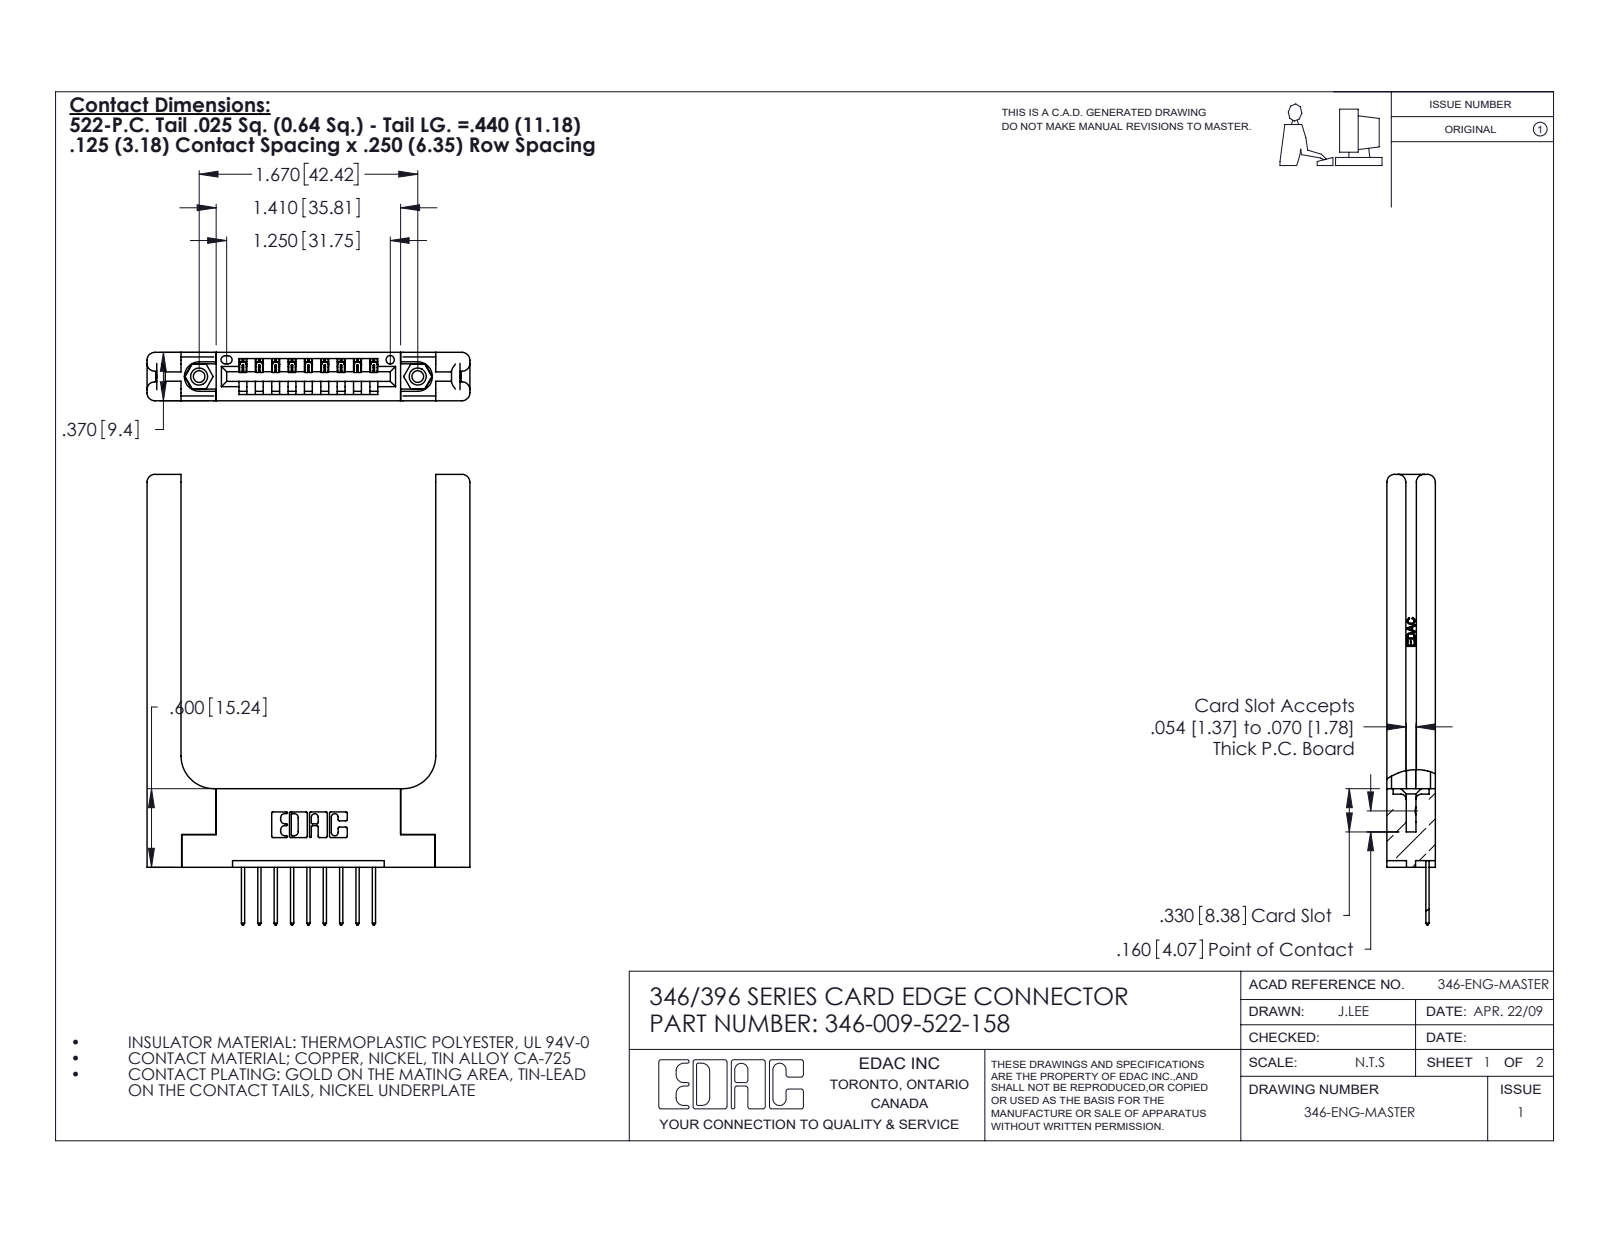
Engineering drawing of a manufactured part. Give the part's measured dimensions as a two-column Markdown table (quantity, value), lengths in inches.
| quantity | value |
| --- | --- |
| part name | 345-250-001_345-250-001-102; 346 Part_Flush Mounting Lugs - 0.156 Dia-TH; 346-220-058_345-220-058; 346-009-522-158 (+1 more) |
| STEP written by | SolidWorks 2020 (CONFIG_CONTROL_DESIGN) |
| units | inches |
| bodies | 14 solids, 914 faces (598 planar, 256 cylindrical, 60 other) |
| overall size | 3.44 × 2.466 × 0.37 |
| volume | 0.81 in³ |
| surface area | 18.7 in² |
| round holes (diameter × count) | 0.089 × 2, 0.125 × 2, 0.156 × 2, 0.064 × 1 |
| round bosses / shafts (diameter × count) | 0.155 × 2 |
| partial cylindrical surfaces (radius × count) | 0.01 × 22, 0.006 × 18, 0.01 × 18, 0.06 × 16, 0.007 × 6, 0.031 × 6, 0.026 × 3, 0.03 × 2 |
| main face-to-face distances | 0.37, 0.15, 0.072, 0.22, 0.148, 0.25, 0.048, 0.322, 0.102, 0.173 |
| hole center spacings | 0.246, 1.465, 1.67 |
